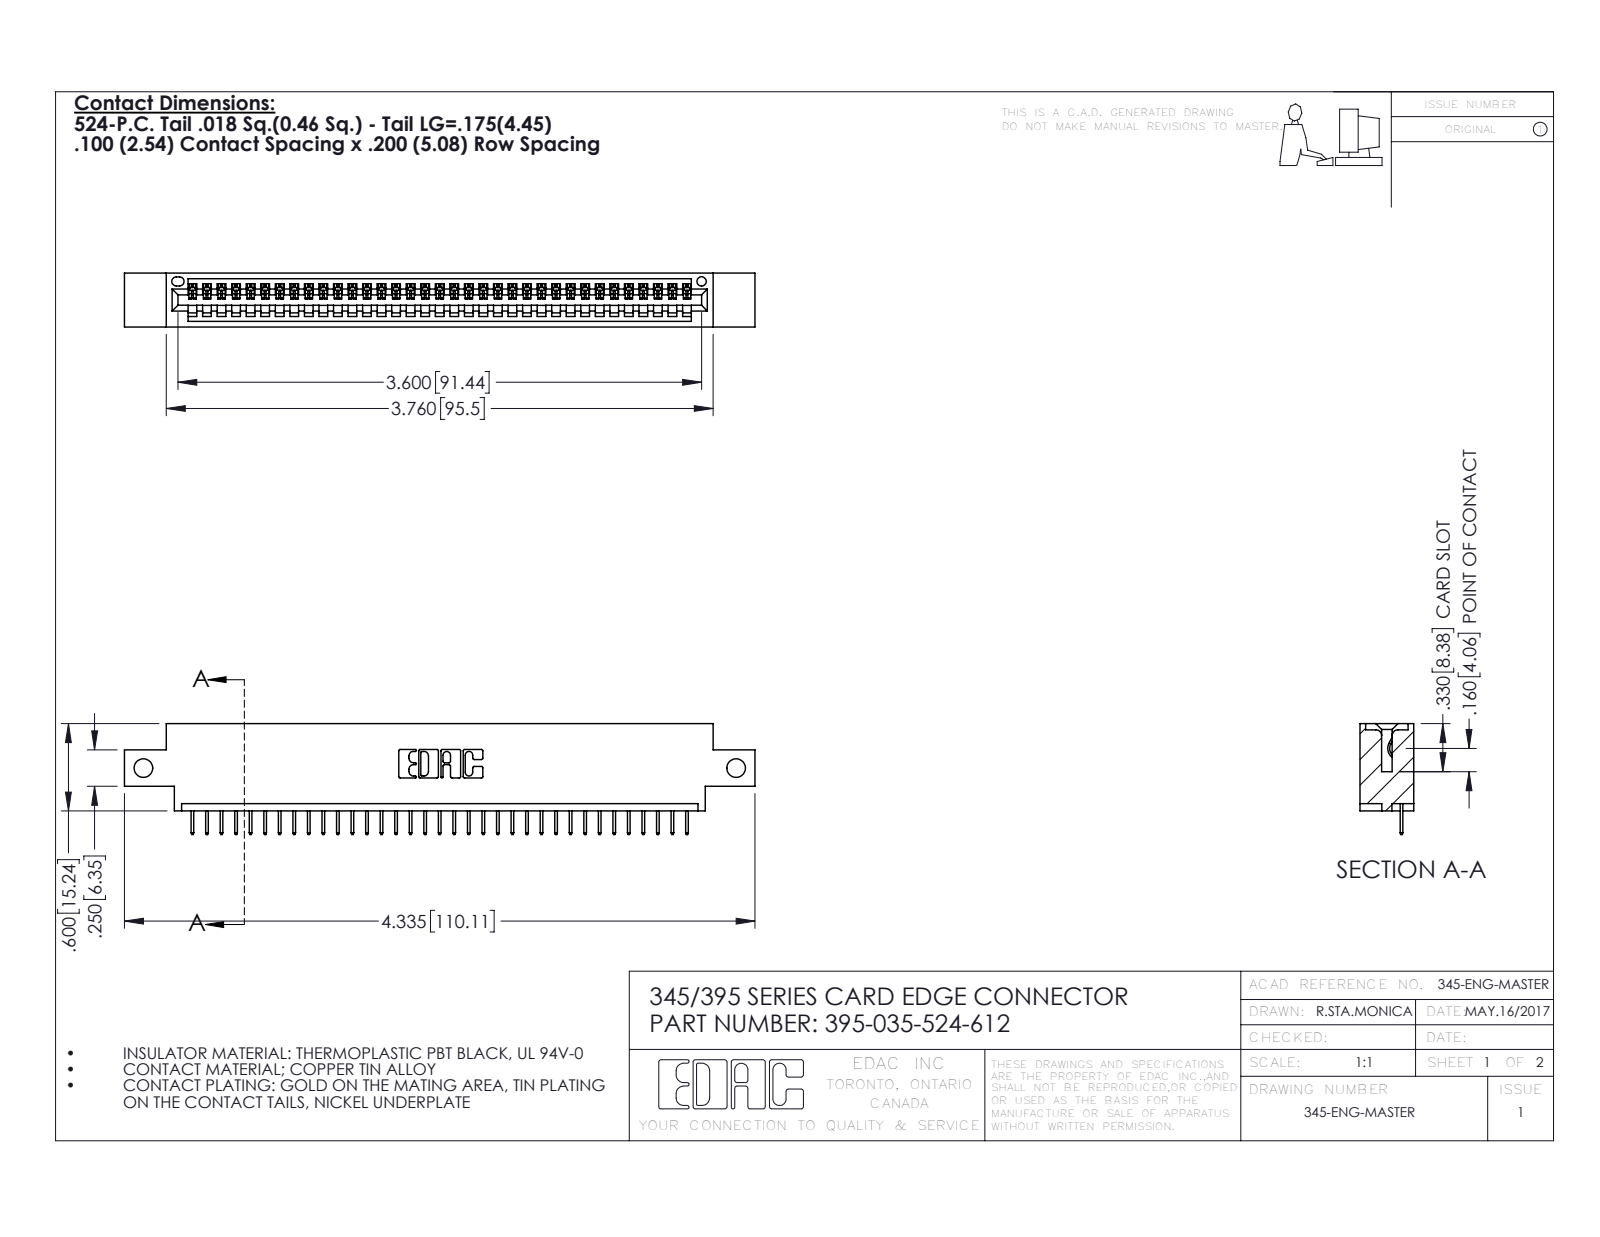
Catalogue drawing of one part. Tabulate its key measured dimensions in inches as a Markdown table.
| quantity | value |
| --- | --- |
| part name | 345-292-001_345-293-124; 395-035-524-612; 345 Part_0.170 Offset - Side Mount |
| STEP written by | SolidWorks 2016 (CONFIG_CONTROL_DESIGN) |
| units | inches |
| bodies | 36 solids, 2300 faces (1694 planar, 606 cylindrical, 0 other) |
| overall size | 4.335 × 0.762 × 0.37 |
| volume | 0.614 in³ |
| surface area | 19.87 in² |
| round holes (diameter × count) | 0.128 × 2, 0.064 × 1 |
| partial cylindrical surfaces (radius × count) | 0.006 × 70, 0.01 × 22, 0.007 × 6, 0.031 × 6, 0.026 × 3, 0.031 × 2, 0.04 × 2, 0.014 × 1 |
| main face-to-face distances | 0.072, 0.298, 0.37, 0.2, 0.098, 0.272, 0.025, 0.225, 0.072, 0.175 |
| hole center spacings | 4.075 |
